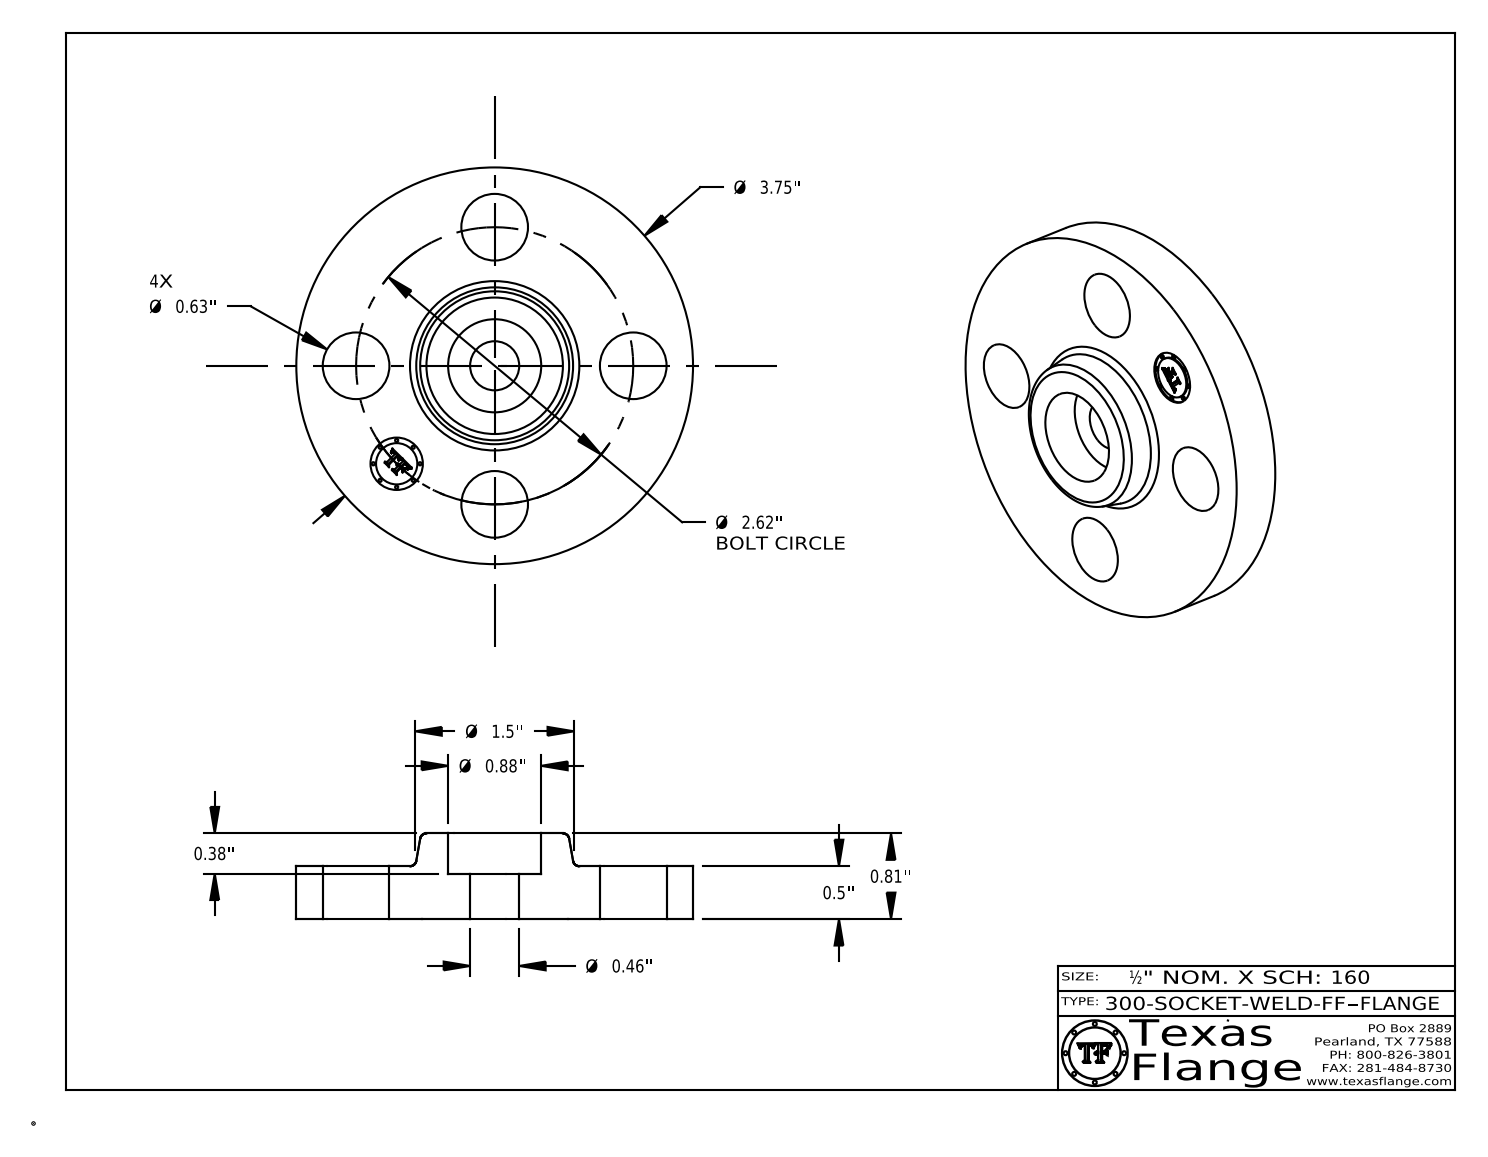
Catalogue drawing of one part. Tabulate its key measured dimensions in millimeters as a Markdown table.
| quantity | value |
| --- | --- |
| part name | 300-SOCKET-WELD-FF |
| STEP written by | CATIA V5 STEP AP214 (AUTOMOTIVE_DESIGN) |
| units | millimeters |
| bodies | 1 solid, 410 faces (370 planar, 34 cylindrical, 6 other) |
| overall size | 95.3 × 95.3 × 20.6 |
| volume | 83 620 mm³ |
| surface area | 20 580 mm² |
| round holes (diameter × count) | 16 × 4, 11.8 × 1, 12.6 × 1, 22.4 × 1 |
| round bosses / shafts (diameter × count) | 0.8 × 8, 95.3 × 1, 9.9 × 1 |
| main face-to-face distances | 12.7, 20.6, 7.9, 1.8, 10.9, 9.7, 12.3, 1.4, 0.4, 8.3 |
| hole center spacings | 33.3, 47, 25.5, 61.5, 66.5, 33.3 |
